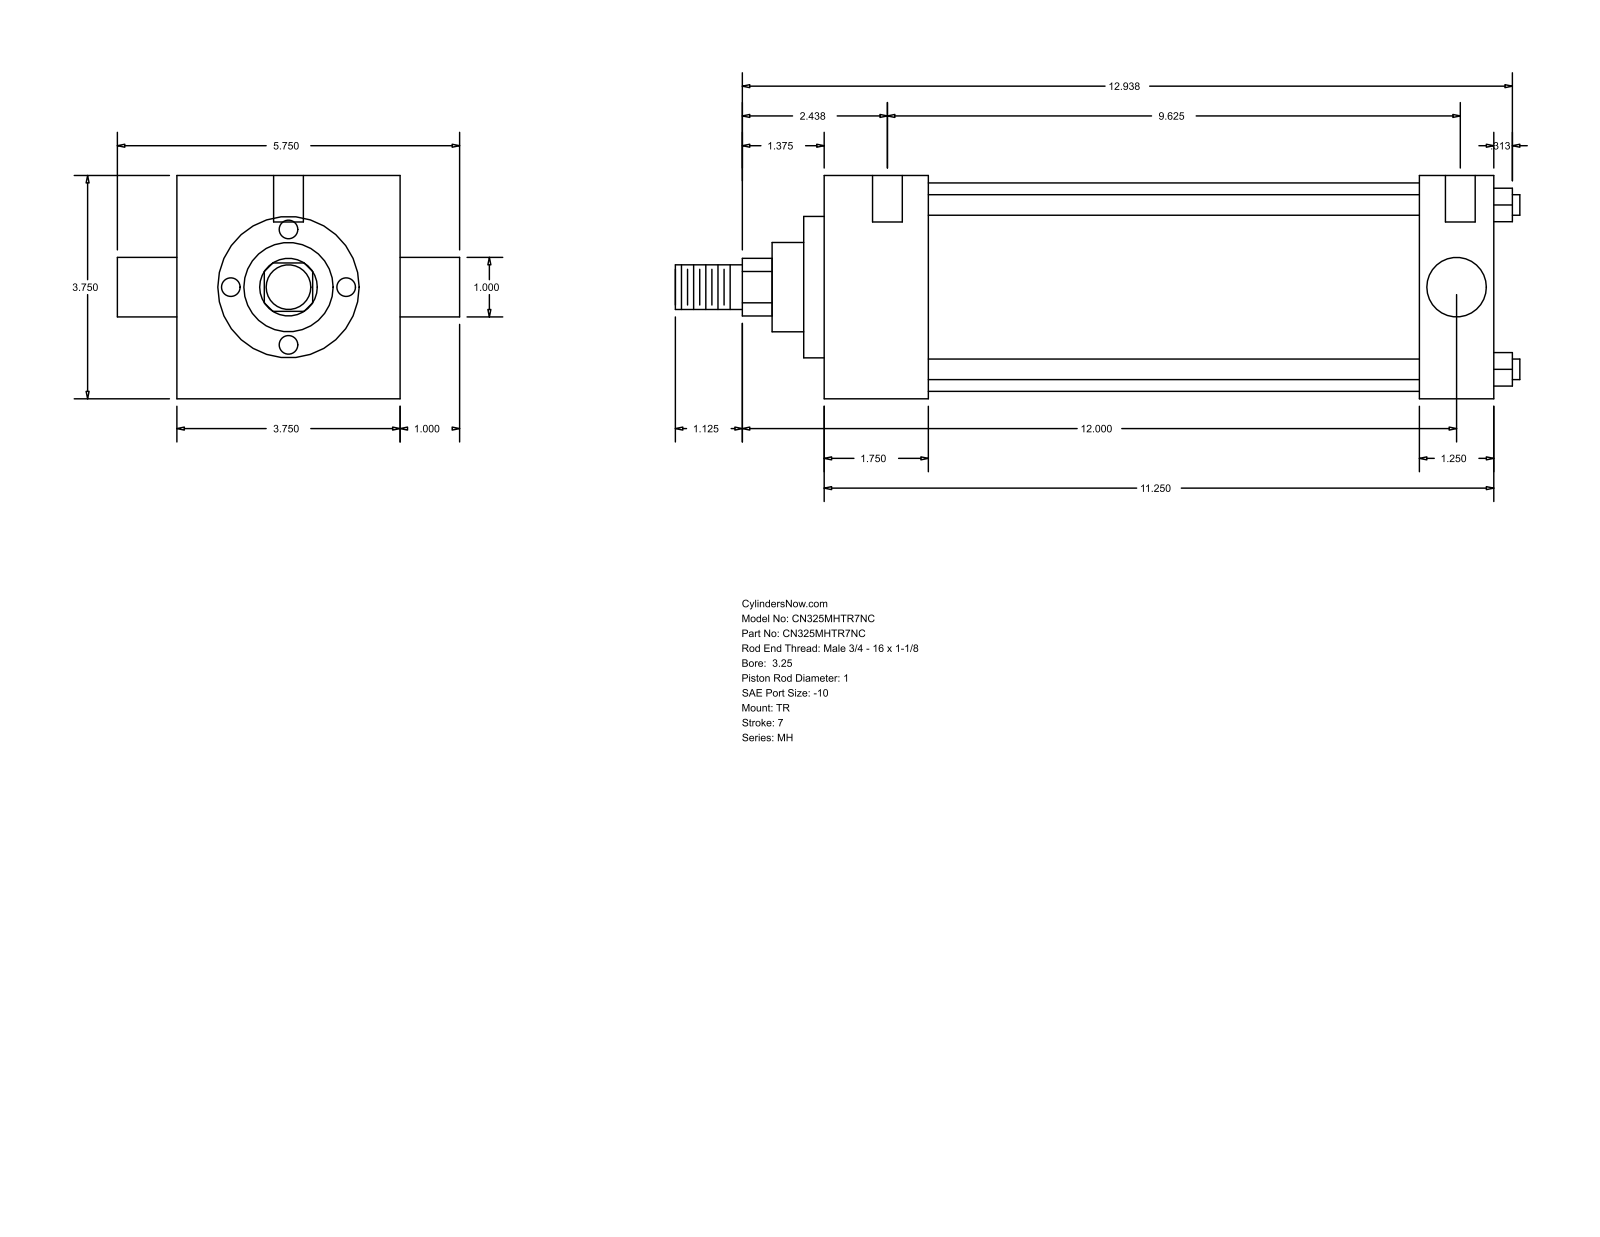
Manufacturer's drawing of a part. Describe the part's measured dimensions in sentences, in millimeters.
The part is named "MH_TR__0325_1". Its 3-D file was written by "GSSL Pune (CONFIG_CONTROL_DESIGN)". It is 0 solids with 86 faces: 61 planar, 25 cylindrical and 0 other. Overall it measures 360.36 by 146.05 by 95.25 millimeters. Round holes: 3 of diameter 5.56, 2 of diameter 12.7. Round bosses or shafts: 4 of diameter 8.76, 2 of diameter 25.4, 1 of diameter 88.9, 1 of diameter 60.33, 1 of diameter 38.1, 1 of diameter 19.05. Partial cylindrical surfaces (rounded edges, fillets, slot ends): 1 of radius 12.29. The main face-to-face distances are 95.24, 285.76, 44.46, 254.01, 209.55, 241.3, 31.75, 8.73, 53.19, 262.74. The hole center spacings are 1.58, 4.76, 244.48, 246.06, 249.24, 250.82.
